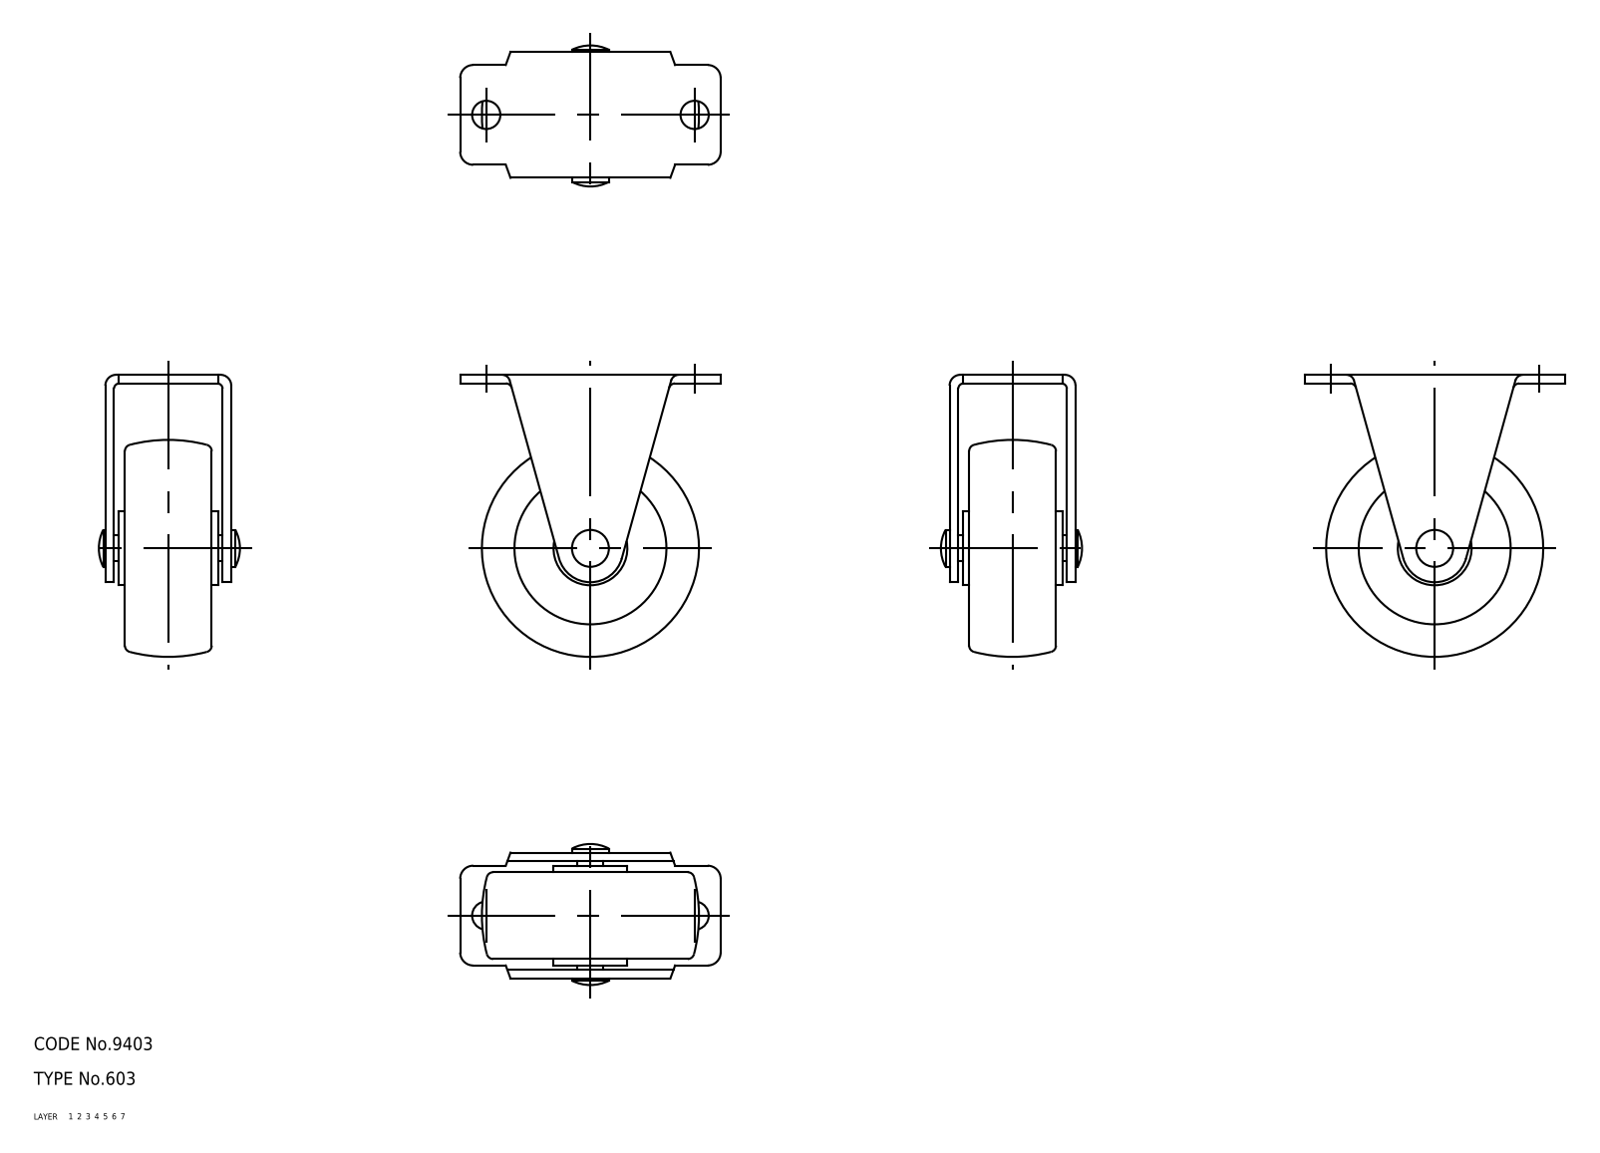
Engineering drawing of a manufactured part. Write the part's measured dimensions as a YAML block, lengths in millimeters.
part_name: "wheel; axle; No_603_14016_36"
step_written_by: "CADfix (AUTOMOTIVE_DESIGN)"
units: millimeters
bodies: {solids: 3, faces: 101, planar: 0, cylindrical: 0, other: 101}
overall_size: [65, 60, 32.5]
volume: 42962
surface_area: 16334
